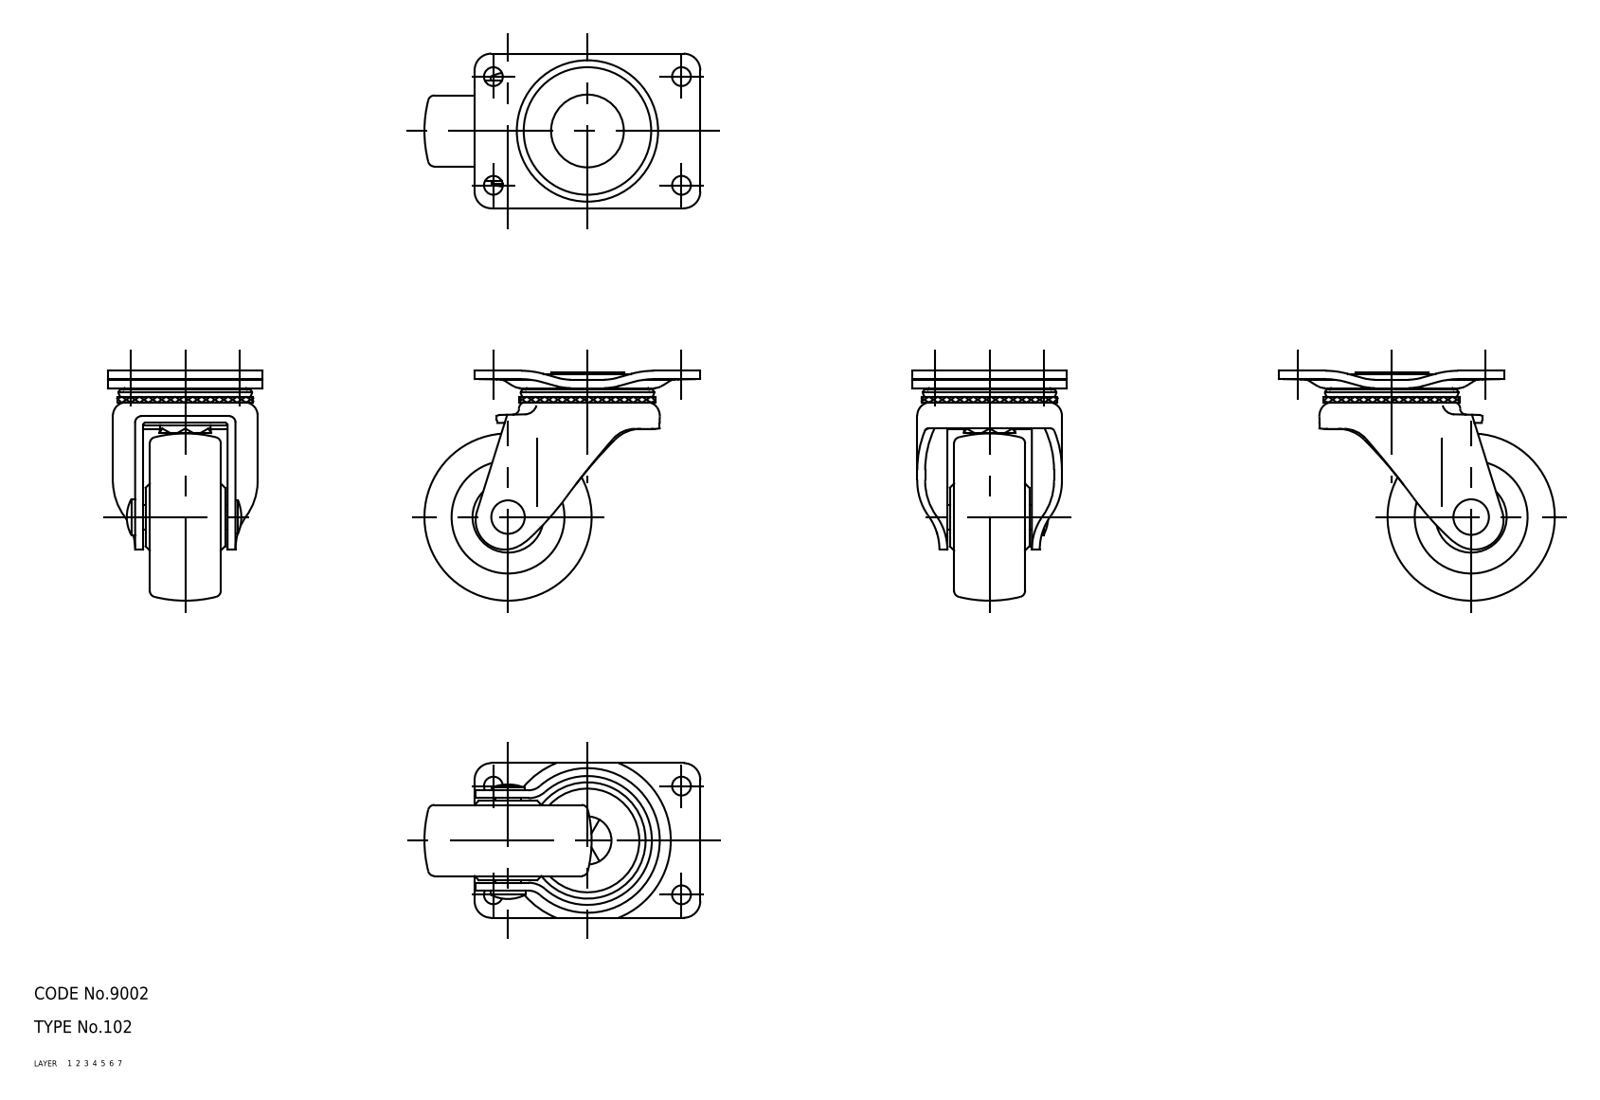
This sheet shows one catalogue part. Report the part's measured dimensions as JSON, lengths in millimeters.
{"part_name": "wheel; mounting plate; main shaft; axle (+1 more)", "step_written_by": "CADfix (AUTOMOTIVE_DESIGN)", "units": "millimeters", "bodies": {"solids": 5, "faces": 256, "planar": 0, "cylindrical": 0, "other": 256}, "overall_size": [66, 55, 37], "volume_mm3": 35115, "surface_area_mm2": 17407}
